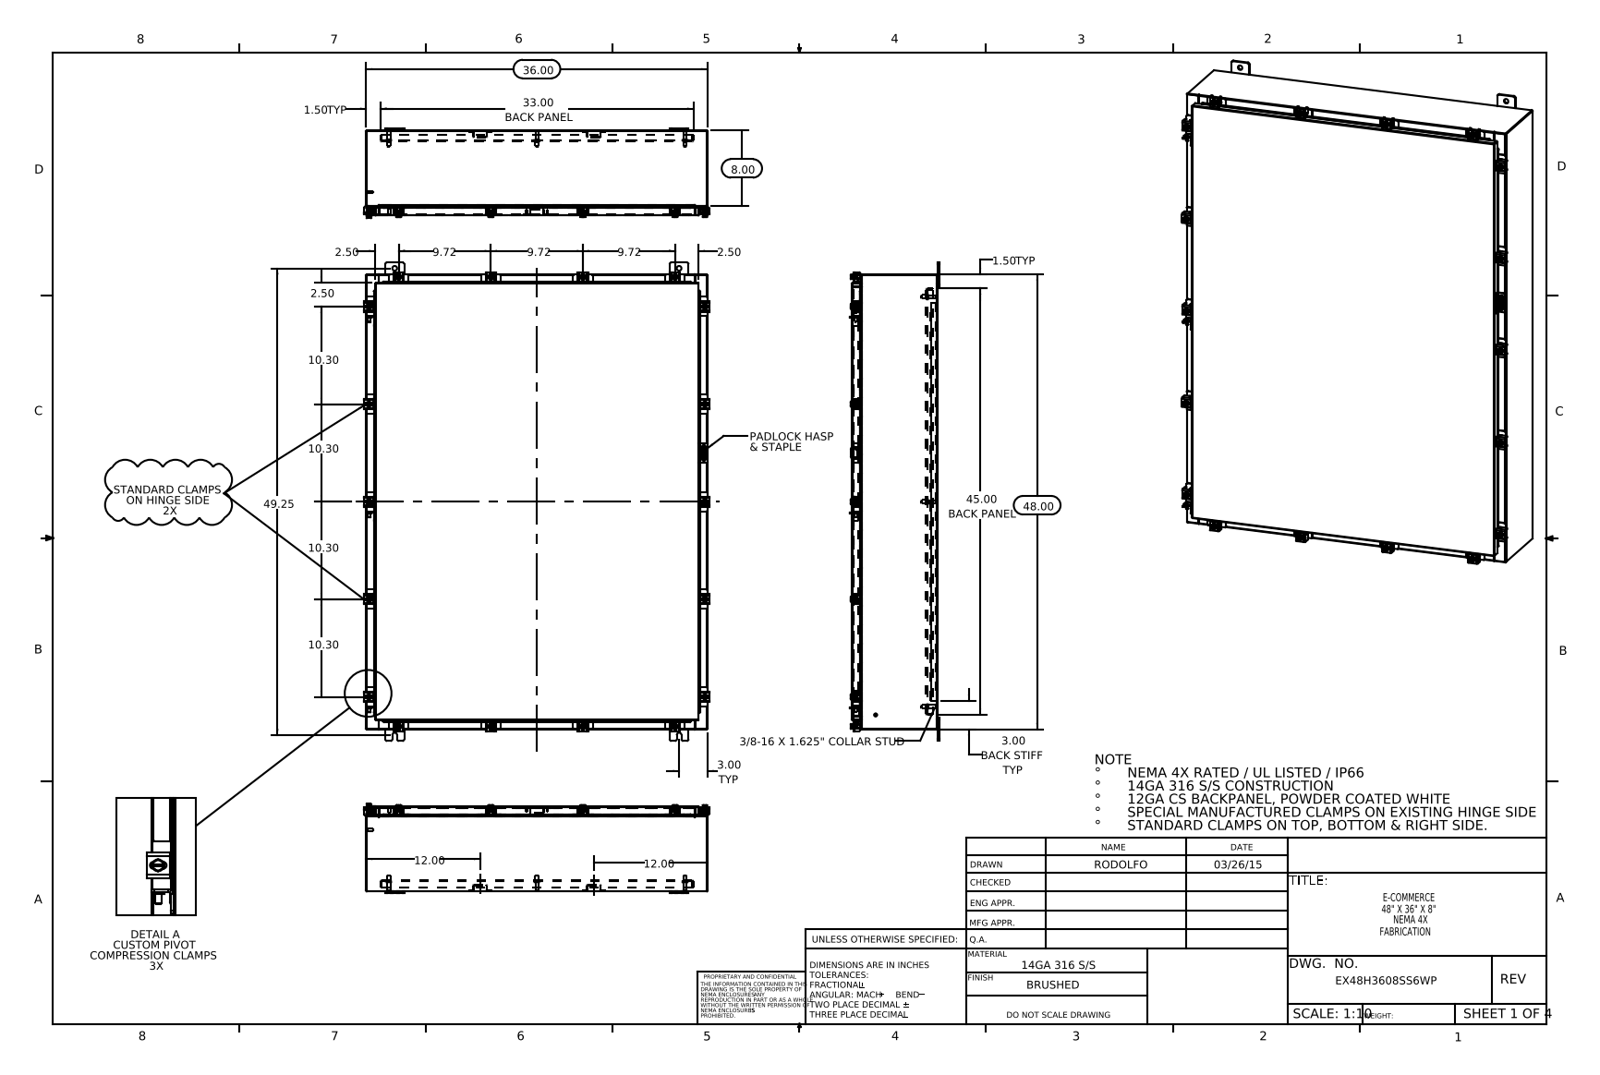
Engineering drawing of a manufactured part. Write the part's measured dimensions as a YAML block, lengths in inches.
part_name: "EX48H3608SS6WP Body; EX48H3608SS6WP Special Clamp; Special Clamp Assembly; 22104005_DEFAULT_RTP30 (+8 more)"
step_written_by: "SolidWorks 2014 (CONFIG_CONTROL_DESIGN)"
units: inches
bodies: {solids: 126, faces: 3106, planar: 1613, cylindrical: 1195, other: 298}
overall_size: [50.5, 36.421, 9.453]
volume: 598.6
surface_area: 14796
round_holes:
  - {diameter: 0.213, count: 18}
  - {diameter: 0.26, count: 18}
  - {diameter: 0.5, count: 12}
  - {diameter: 0.25, count: 7}
  - {diameter: 0.125, count: 1}
round_bosses_or_shafts:
  - {diameter: 0.5, count: 18}
  - {diameter: 0.25, count: 18}
  - {diameter: 0.399, count: 15}
  - {diameter: 0.625, count: 8}
  - {diameter: 0.375, count: 8}
  - {diameter: 0.33, count: 8}
  - {diameter: 0.157, count: 6}
  - {diameter: 0.14, count: 6}
partial_cylinders:
  - {radius: 0.06, count: 76}
  - {radius: 0.013, count: 38}
  - {radius: 0.141, count: 36}
  - {radius: 0.088, count: 34}
  - {radius: 0.12, count: 33}
  - {radius: 0.09, count: 27}
  - {radius: 0.05, count: 25}
  - {radius: 0.145, count: 24}
face_to_face_distances: [0.075, 8.9, 8.826, 8.975, 0.104, 1, 1.075, 7.826, 7.9, 1.179]
hole_center_spacings: [1.969, 2.347, 4.44, 13.972, 14.728, 16.126, 16.624, 17.756]
